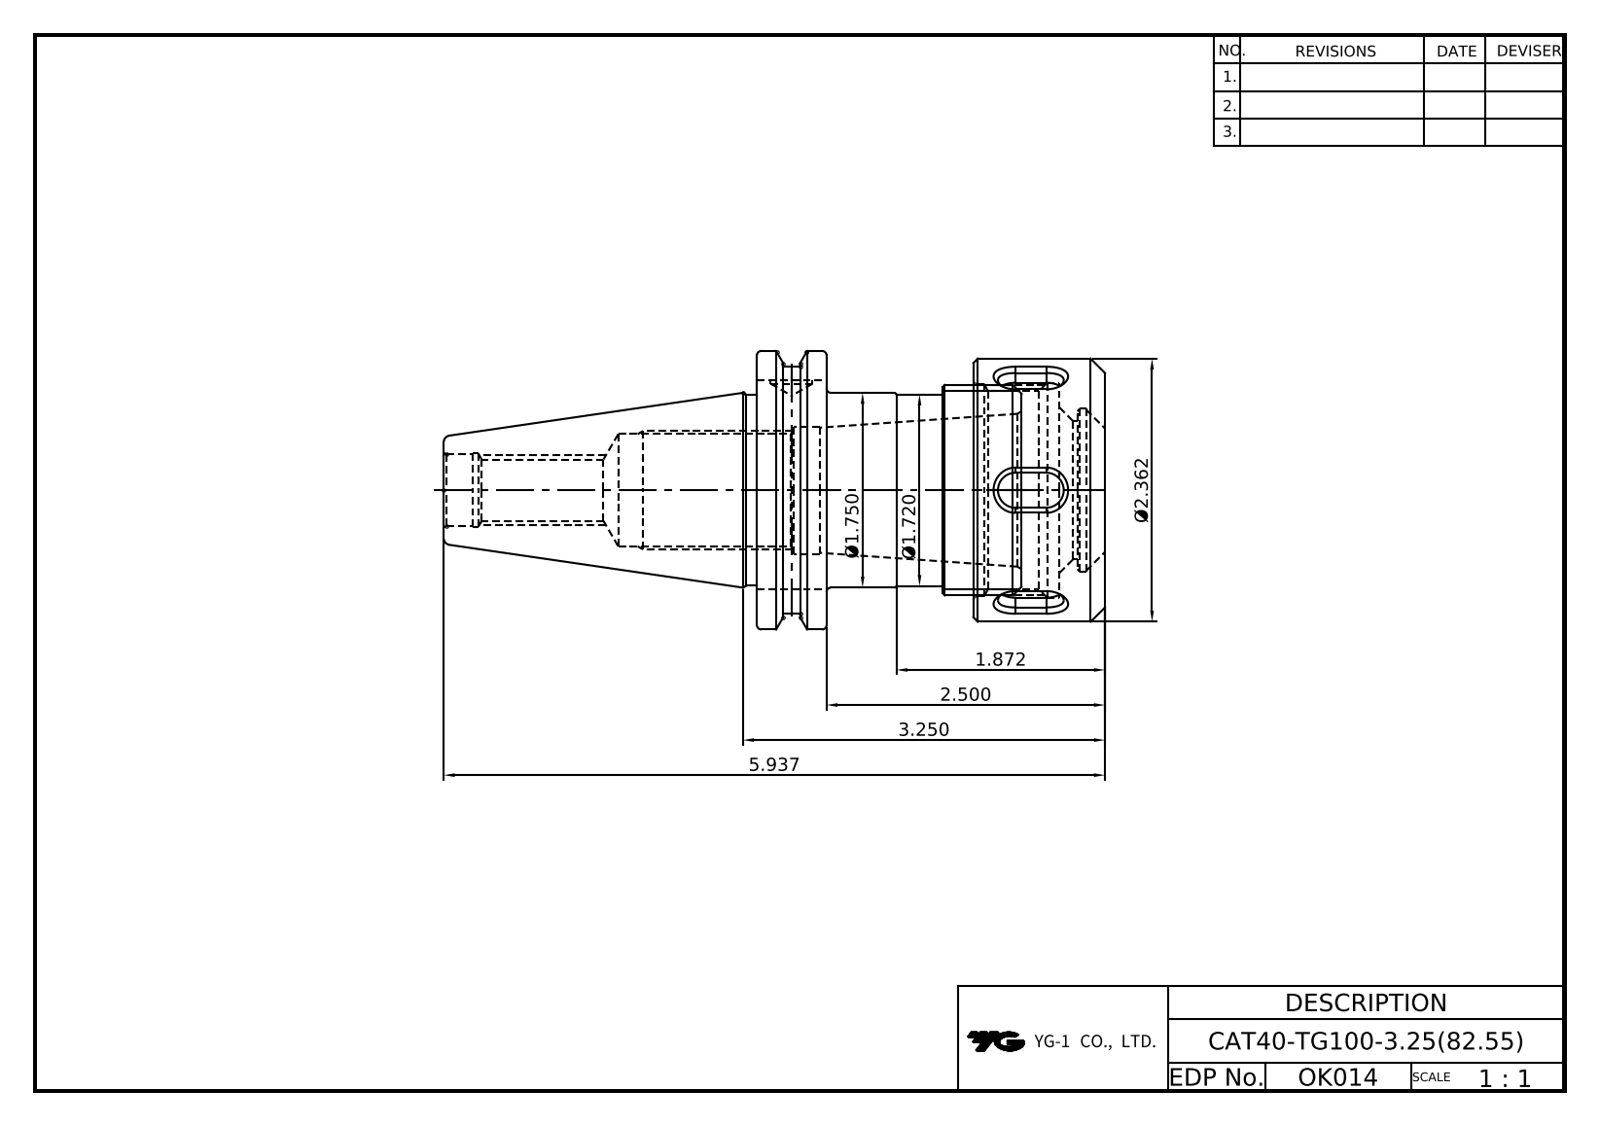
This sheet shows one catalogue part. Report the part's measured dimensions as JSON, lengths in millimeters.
{"part_name": "LO-CAT40-TG100-82.55; TG100 NUT", "step_written_by": "Autodesk Inventor 2025 (AP242_MANAGED_MODEL_BASED_3D_ENGINEERING_MIM_LF)", "units": "millimeters", "bodies": {"solids": 2, "faces": 71, "planar": 34, "cylindrical": 18, "other": 19}, "overall_size": [150.8, 63.5, 61.09], "volume_mm3": 177206, "surface_area_mm2": 46618, "round_holes": [[9.53, 1], [13.39, 1], [16.3, 1], [18.92, 1], [29, 1], [35, 1], [48, 1]], "round_bosses_or_shafts": [[63.5, 1], [60, 1], [56.3, 1], [47.62, 1], [44.45, 1], [43.7, 1], [43.6, 1]], "face_to_face_distances": [19, 44.5, 63.5, 15.88, 60.38, 79.38, 44.38, 28.5, 16, 35]}
